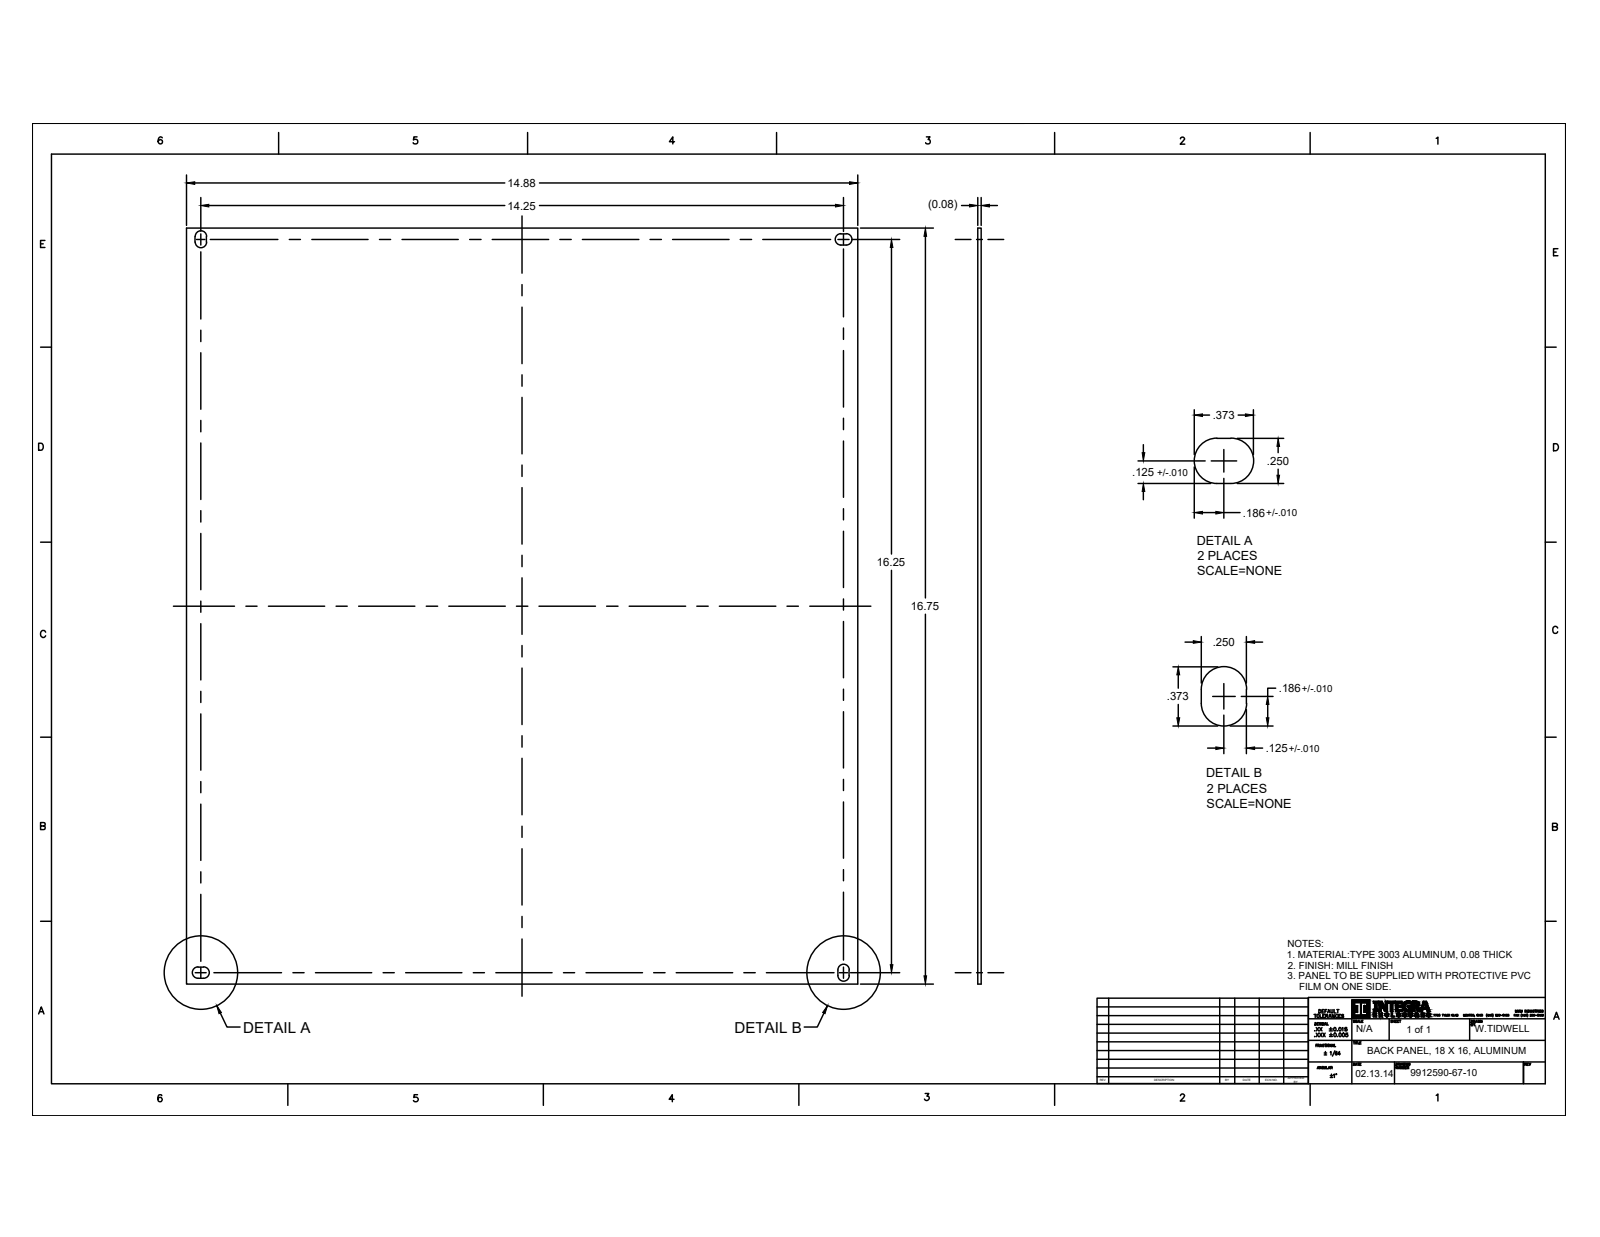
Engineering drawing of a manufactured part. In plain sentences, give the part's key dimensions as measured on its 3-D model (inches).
The part is named "ABP-1816-P10". Its 3-D file was written by "SolidWorks 2018 (AUTOMOTIVE_DESIGN)". It is 1 solid with 22 faces: 14 planar, 8 cylindrical and 0 other. Overall it measures 16.75 by 14.88 by 0.063 inches. Its volume is 15.68 cubic inches and its surface area 502.1 square inches. Partial cylindrical surfaces (rounded edges, fillets, slot ends): 8 of radius 0.125. The main face-to-face distances are 0.063, 14.88, 16.75, 0.25, 0.19, 0.44, 14.44, 14.69, 14.25, 0.125.
